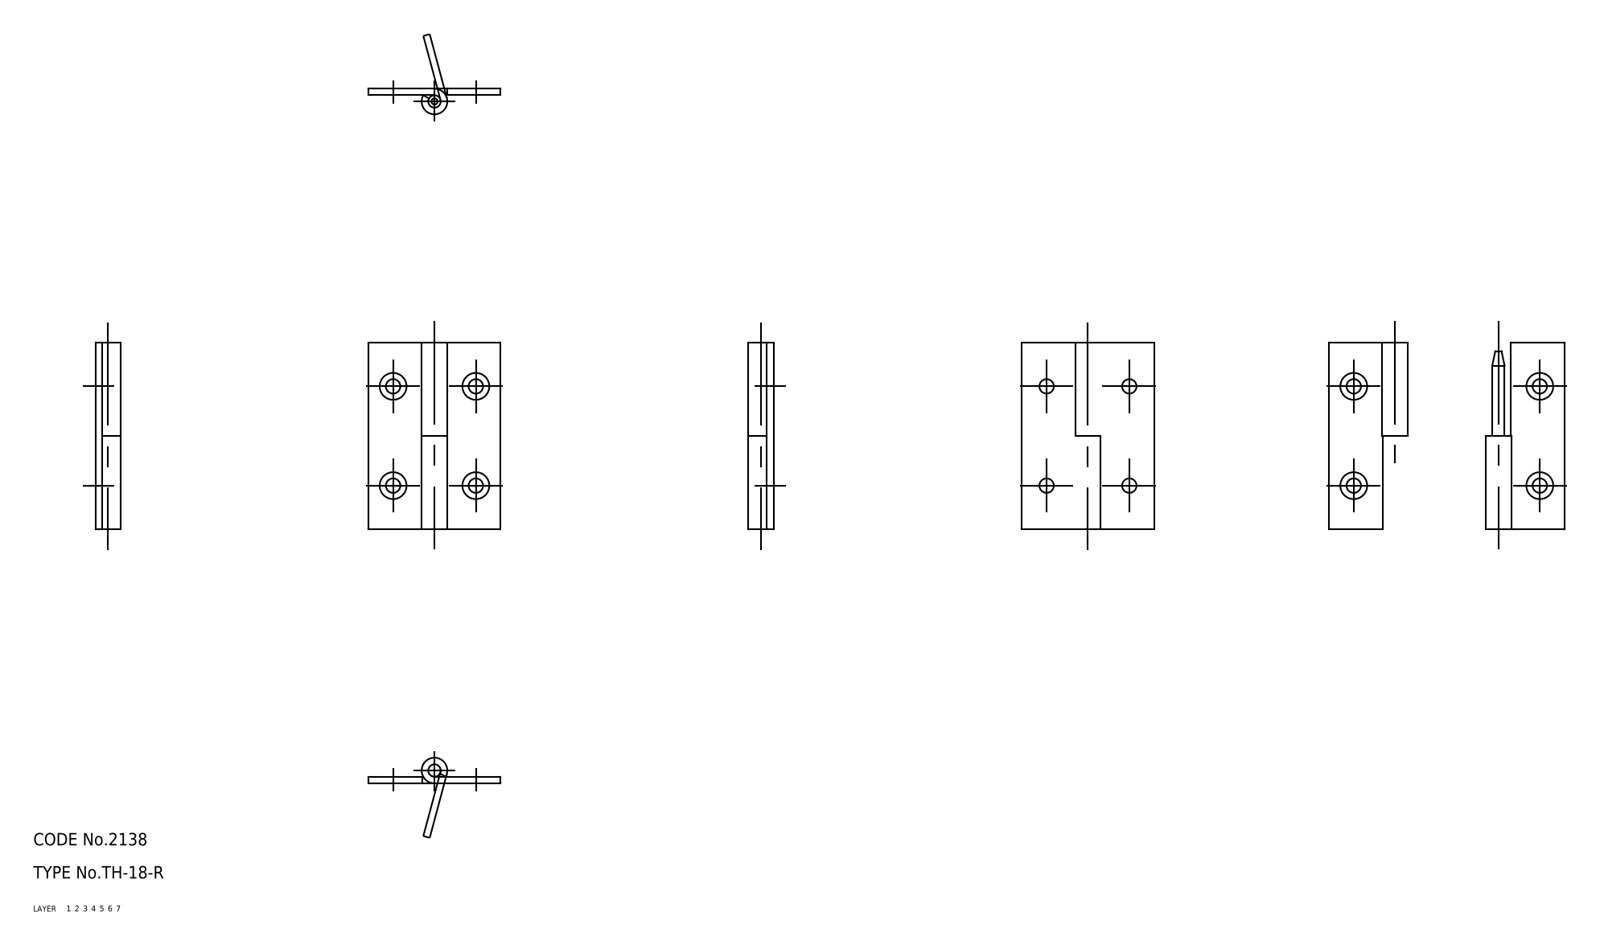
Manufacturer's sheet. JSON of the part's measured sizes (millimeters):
{"part_name": "shaft; hinge piece_B; hinge piece_A; TH_18_R_5937_36", "step_written_by": "CADfix (AUTOMOTIVE_DESIGN)", "units": "millimeters", "bodies": {"solids": 3, "faces": 42, "planar": 0, "cylindrical": 0, "other": 42}, "overall_size": [45, 32, 6.2], "volume_mm3": 3111, "surface_area_mm2": 4517}
